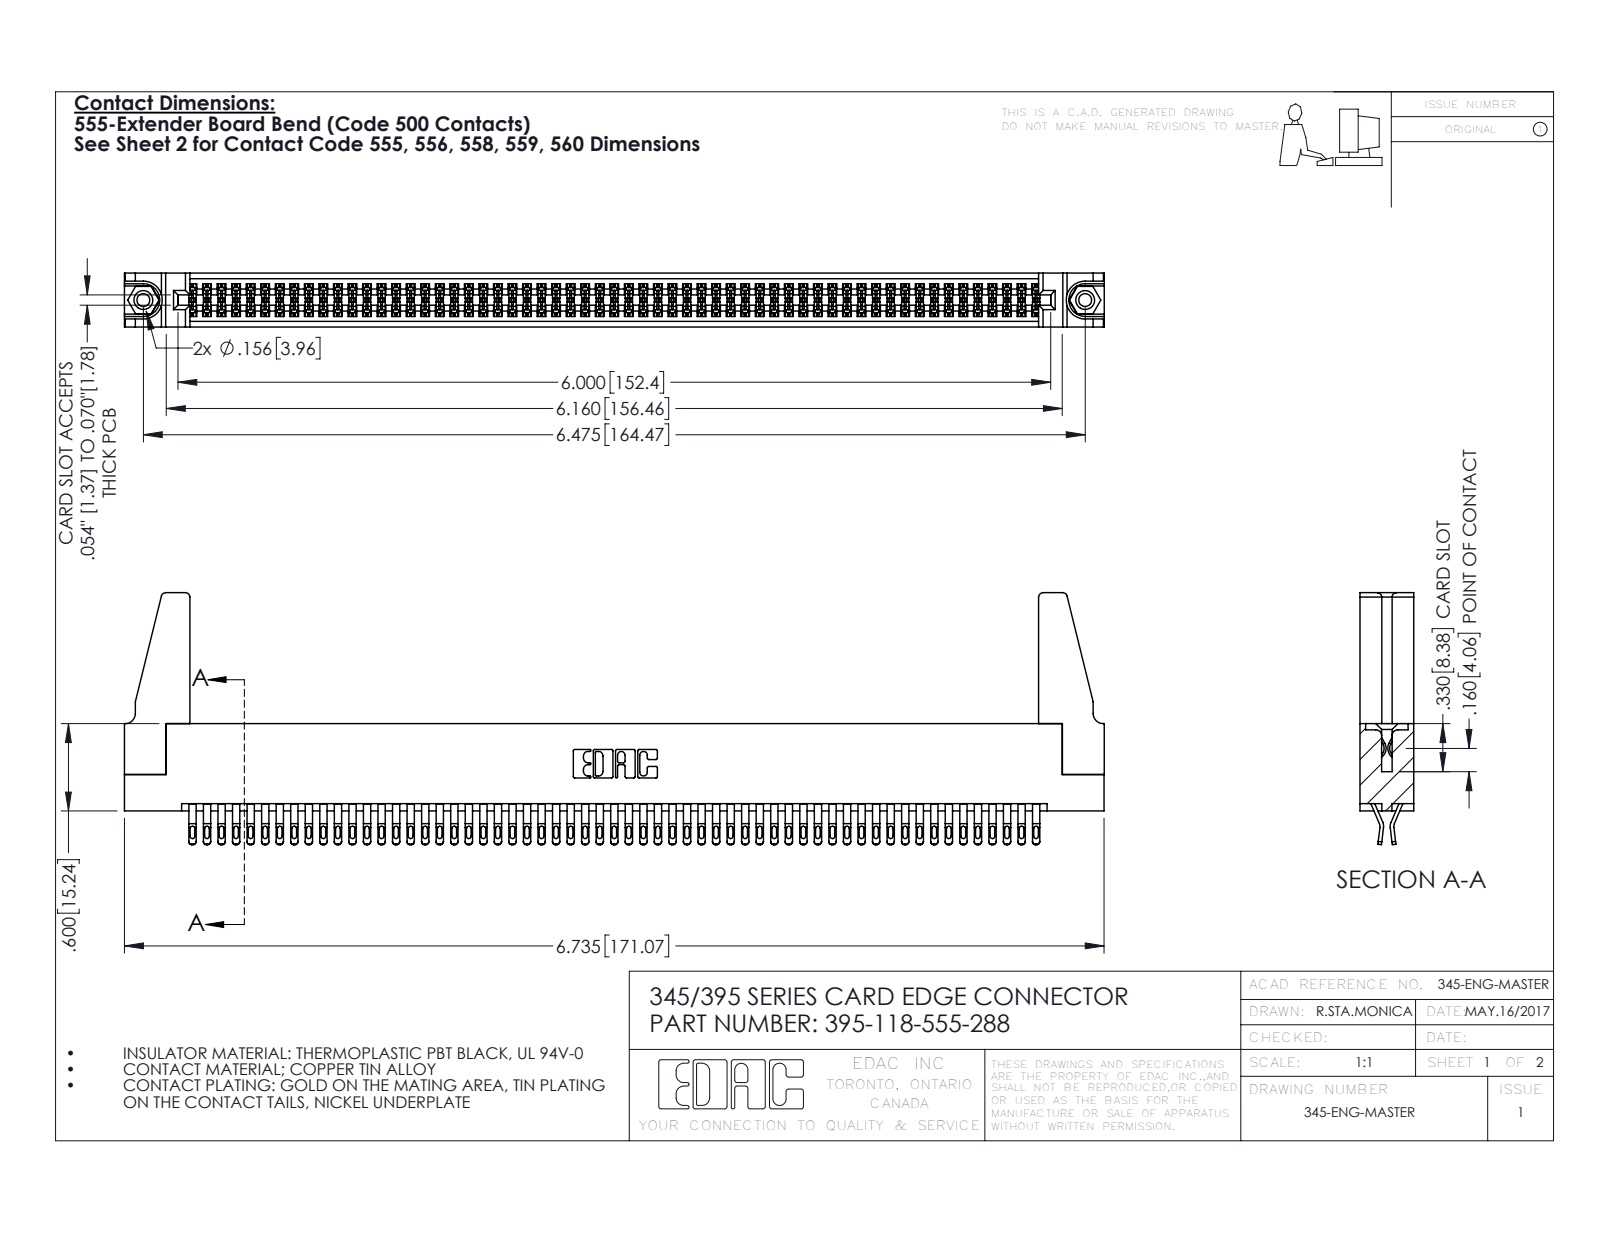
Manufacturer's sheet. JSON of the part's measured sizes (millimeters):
{"part_name": "345-220-078_345-220-088; 345 Part_Flush Mounting Lugs - 0.156 Dia-TH; 395-118-555-288; 345-250-001_345-250-001-102 (+1 more)", "step_written_by": "SolidWorks 2016 (CONFIG_CONTROL_DESIGN)", "units": "millimeters", "bodies": {"solids": 123, "faces": 6858, "planar": 3810, "cylindrical": 3032, "other": 16}, "overall_size": [171.1, 44, 9.4], "volume_mm3": 20370, "surface_area_mm2": 29950, "round_holes": [[2.3, 2], [3.2, 2], [4, 2], [1.6, 1]], "round_bosses_or_shafts": [[3.9, 2]], "partial_cylinders_radius": [[0.4, 295], [0.5, 236], [0.2, 177], [0.3, 22], [0.8, 8], [0.2, 6], [0.8, 6], [0.7, 3]], "face_to_face_distances": [1.8, 7.6, 9.4, 0.6, 5.1, 2.5, 6.9, 5.7, 4.4, 3.8], "hole_center_spacings": [6.9, 158.5, 164.5]}
